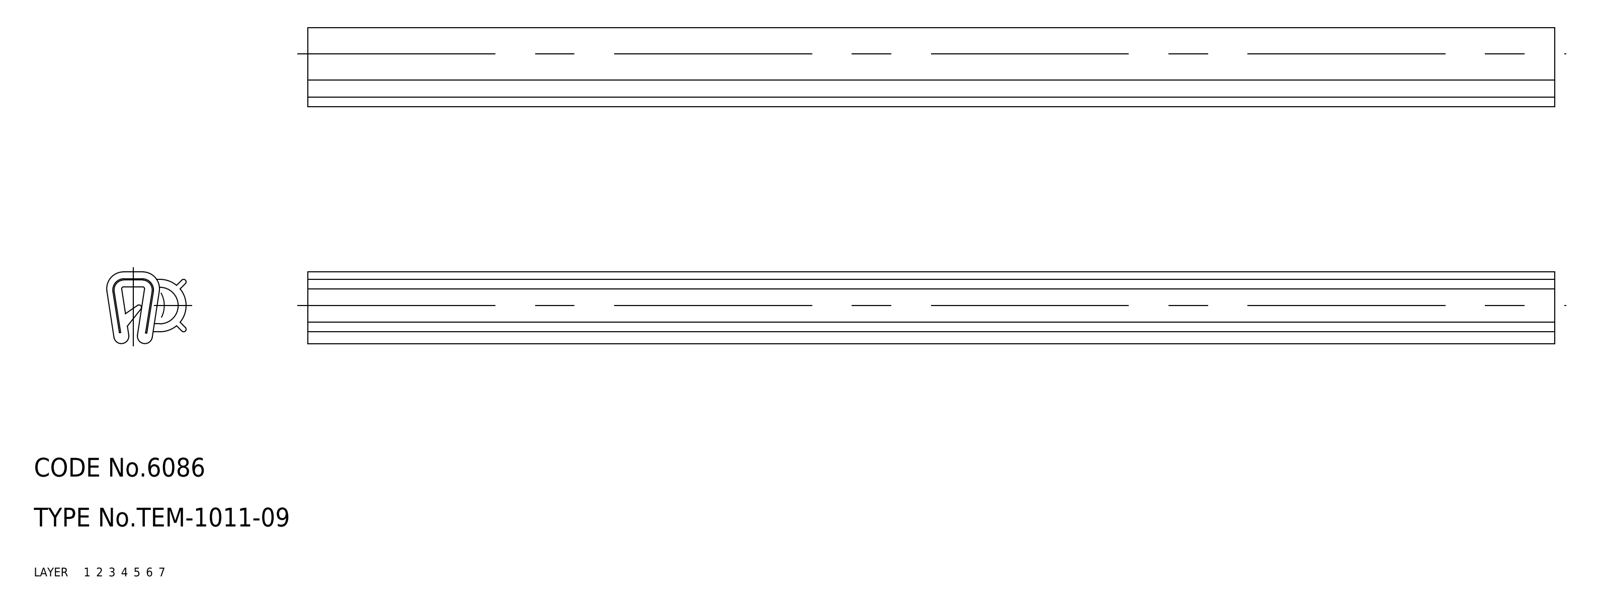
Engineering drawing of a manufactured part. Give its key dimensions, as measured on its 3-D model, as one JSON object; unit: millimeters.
{"part_name": "rubber foam; gasket; center core; TEM_1011_09_30223_36", "step_written_by": "CADfix (AUTOMOTIVE_DESIGN)", "units": "millimeters", "bodies": {"solids": 3, "faces": 62, "planar": 0, "cylindrical": 0, "other": 62}, "overall_size": [200, 12.74, 11.5], "volume_mm3": 16401, "surface_area_mm2": 36473}
